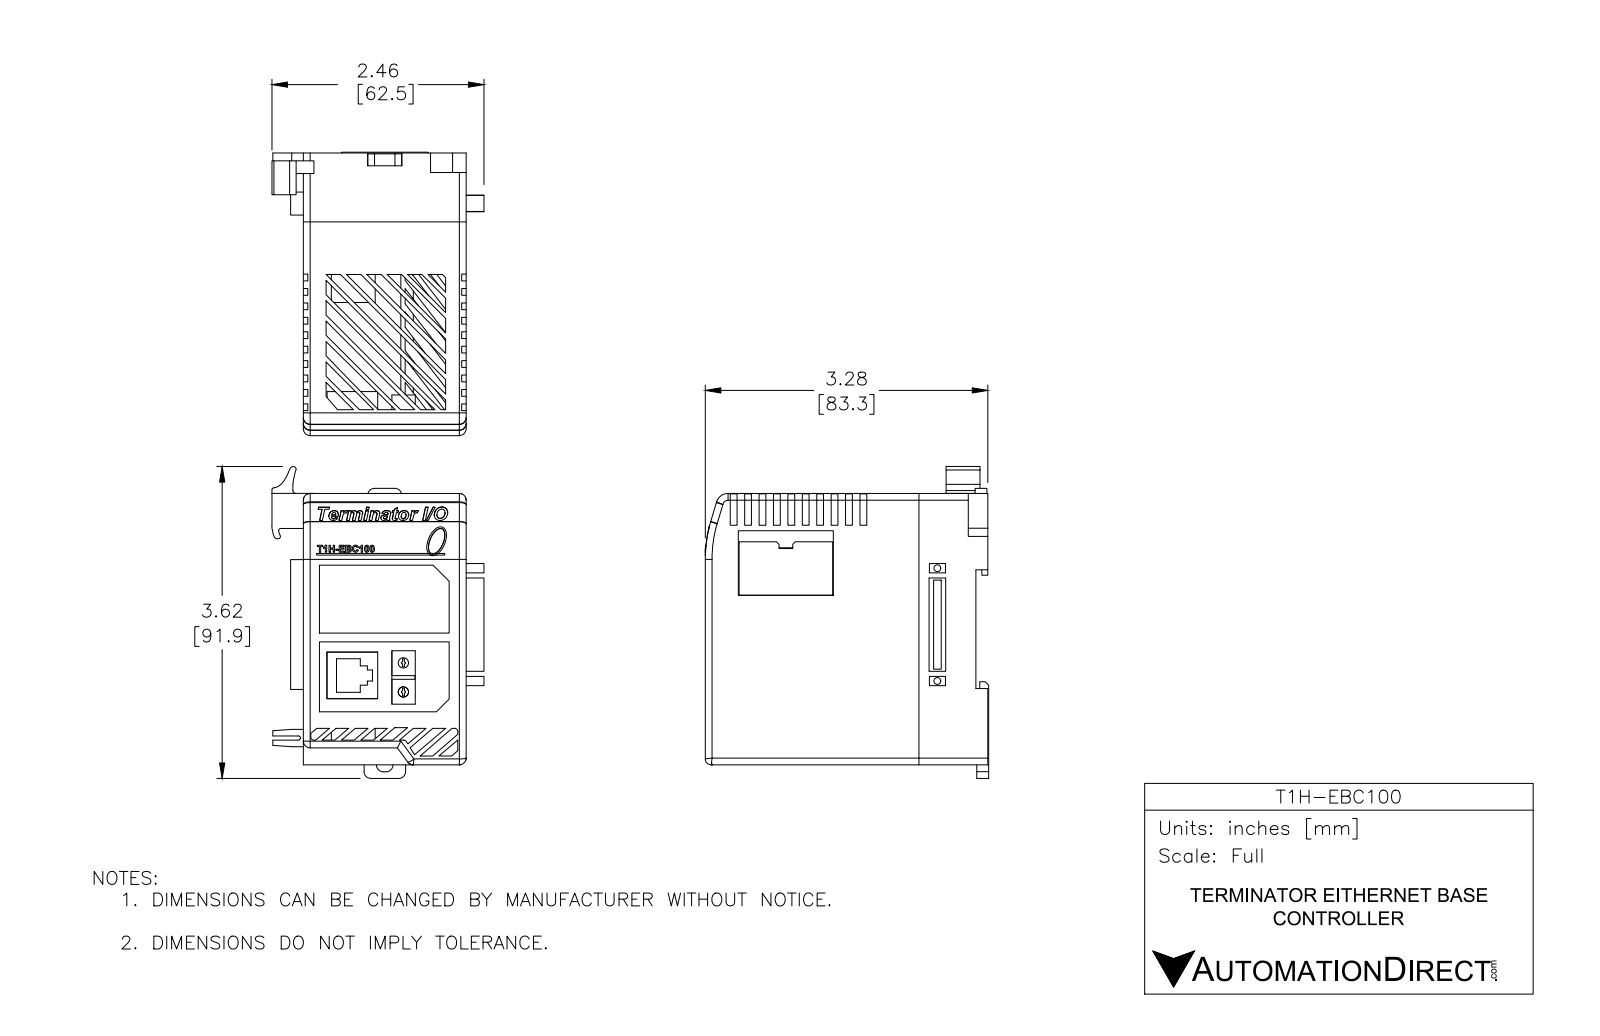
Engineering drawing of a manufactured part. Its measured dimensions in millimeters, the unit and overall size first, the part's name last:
Units: millimetres
Overall size (bounding box): 91.94 × 83.59 × 62.5
Round holes (diameter × count): ⌀2 ×2, ⌀3.01 ×2
Round bosses / shafts (diameter × count): ⌀1.5 ×2, ⌀3.01 ×1
Partial cylindrical surfaces — rounded edges, fillets, slot ends (radius × count): R2 ×18, R1 ×12, R0.75 ×4, R2.06 ×2, R0.83 ×1, R0.94 ×1, R2.02 ×1, R2.04 ×1
Main face-to-face distances: 2, 46, 48, 44, 1, 61, 3.5, 16.8, 77.8, 78
Hole centre spacings: 8.58, 33.25
Volume: 106 206 mm³ · Surface area: 59 260 mm²
Bodies: 25 solids, 1009 faces (741 planar, 72 cylindrical, 196 other)
Part name (STEP PRODUCT): T1H-EBC100
STEP written by: SolidWorks 2013 (AUTOMOTIVE_DESIGN)
